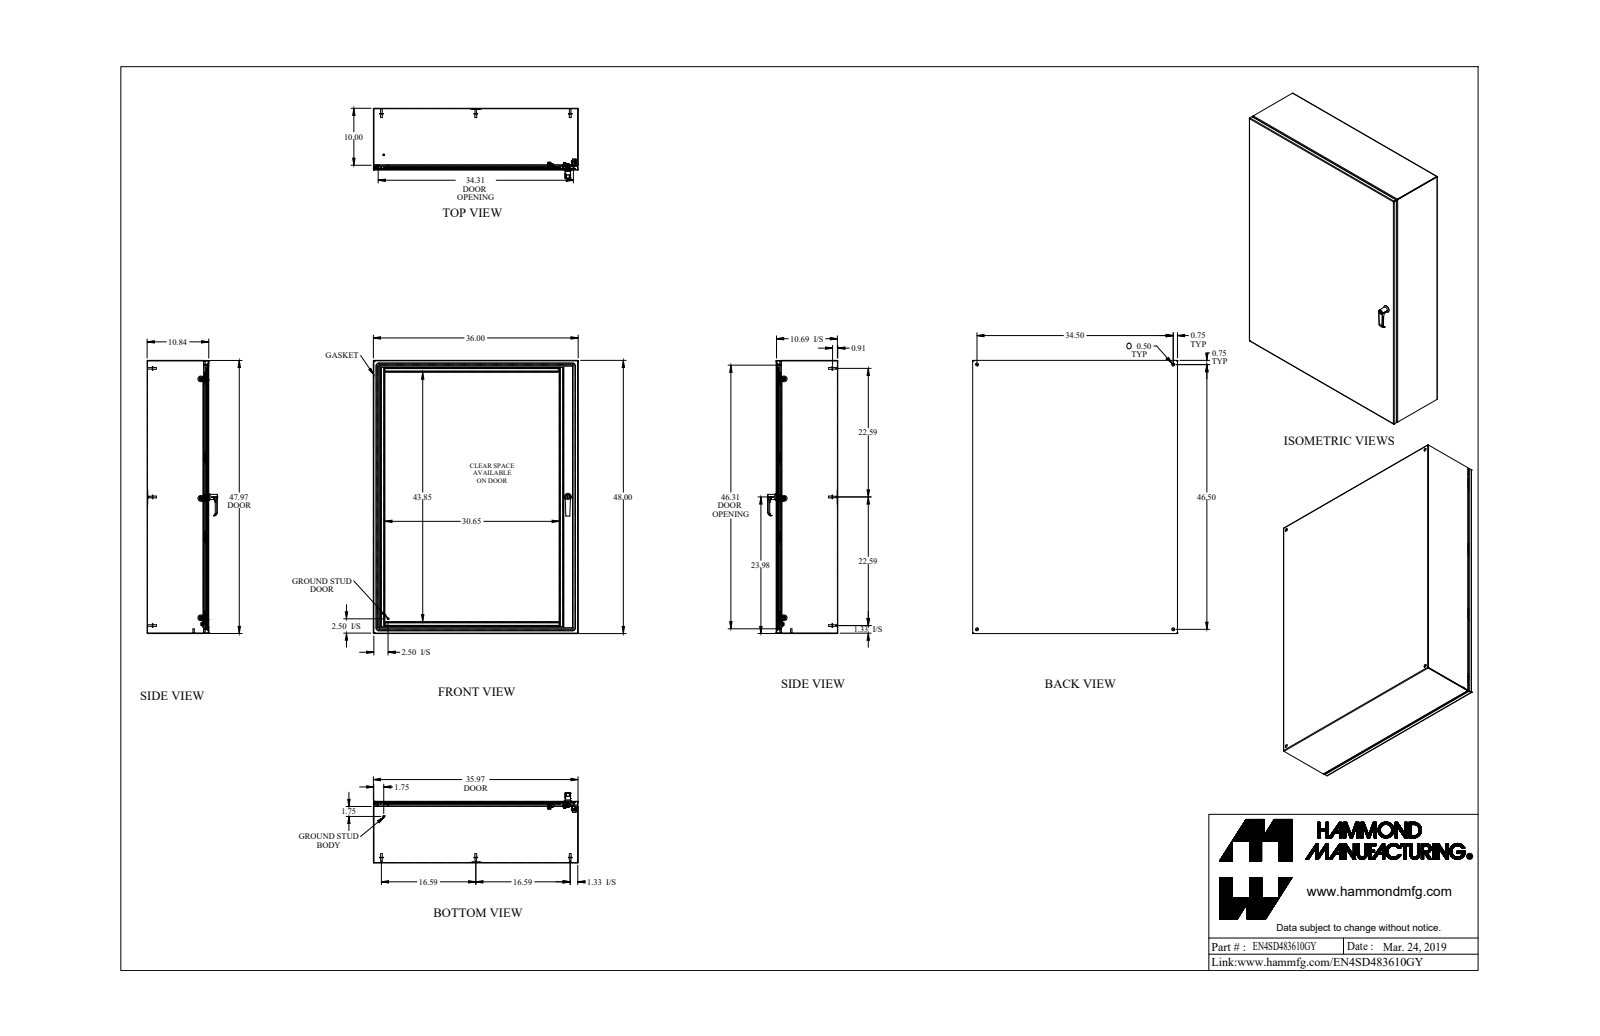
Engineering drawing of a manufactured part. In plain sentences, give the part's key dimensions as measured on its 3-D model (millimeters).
The part is named "EN4SD483610GY". Its 3-D file was written by "SolidWorks 2018 (AUTOMOTIVE_DESIGN)". It is 61 solids with 1733 faces: 757 planar, 638 cylindrical and 338 other. Overall it measures 1219.2 by 914.4 by 314.1 millimeters. Its volume is 7 060 000 cubic millimeters and its surface area 7 774 000 square millimeters. Round holes: 6 of diameter 4.5, 4 of diameter 5, 4 of diameter 12.7, 3 of diameter 6.4, 3 of diameter 6.7, 3 of diameter 10.5, 2 of diameter 6.5, 2 of diameter 8, 2 of diameter 10, 1 of diameter 4.4, 1 of diameter 6.1, 1 of diameter 6.1. Round bosses or shafts: 9 of diameter 15.9, 8 of diameter 8, 8 of diameter 6.9, 7 of diameter 6.4, 6 of diameter 9.5, 6 of diameter 4, 3 of diameter 25.4, 2 of diameter 16. Partial cylindrical surfaces (rounded edges, fillets, slot ends): 24 of radius 1.1, 24 of radius 2.1, 20 of radius 0.9, 20 of radius 2.7, 17 of radius 1.6, 15 of radius 0.8, 10 of radius 2.4, 9 of radius 0.4. The main face-to-face distances are 1.8, 273.4, 271.6, 275.3, 912.6, 910.7, 914.4, 1.8, 1215.5, 1217.4. The hole center spacings are 1066, 20, 532.9, 533.1, 533.4, 851, 876.3, 1181.1.
